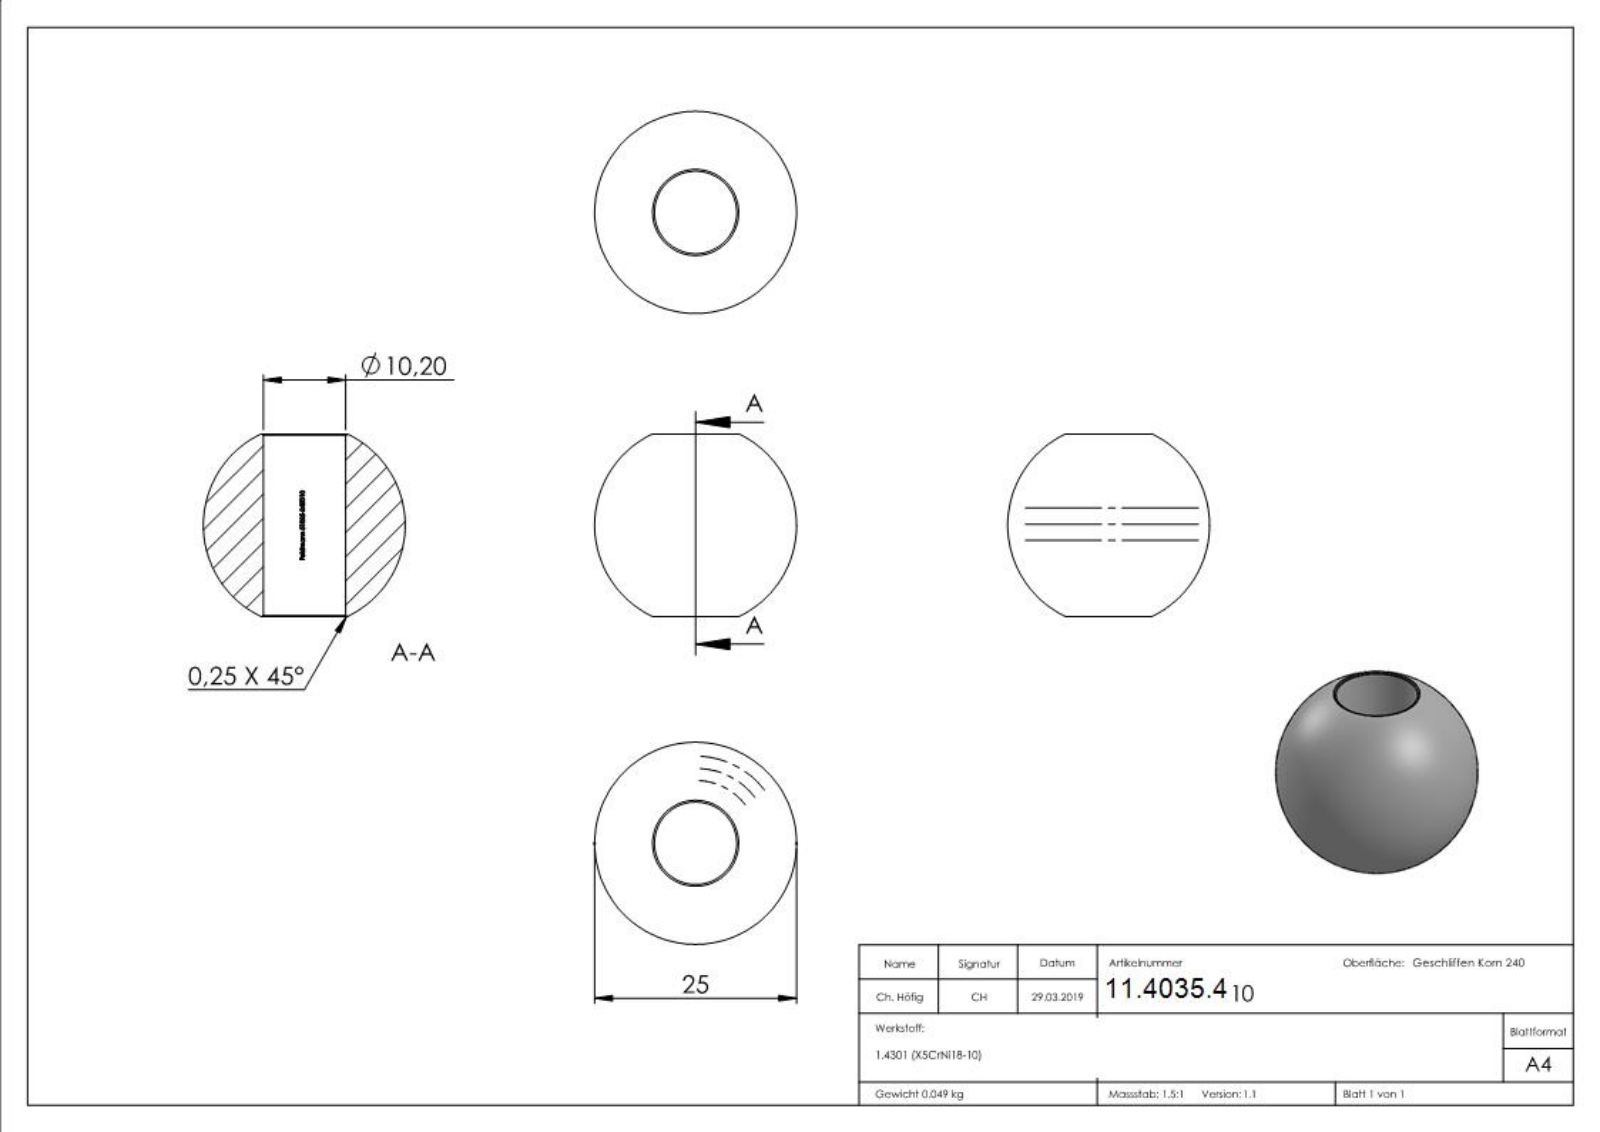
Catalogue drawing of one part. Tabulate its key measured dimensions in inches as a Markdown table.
| quantity | value |
| --- | --- |
| part name | 51025-240D10 |
| STEP written by | SolidWorks 2015 (CONFIG_CONTROL_DESIGN) |
| units | inches |
| bodies | 1 solid, 259 faces (113 planar, 30 cylindrical, 116 other) |
| overall size | 0.984 × 0.984 × 0.891 |
| volume | 0.38 in³ |
| surface area | 3.897 in² |
| round holes (diameter × count) | 0.402 × 1 |
| partial cylindrical surfaces (radius × count) | 0.205 × 1 |
| main face-to-face distances | 0.026, 0.024, 0.254, 0.117, 0.23, 0.05, 0.014, 0.28, 0.137, 0.143 |
